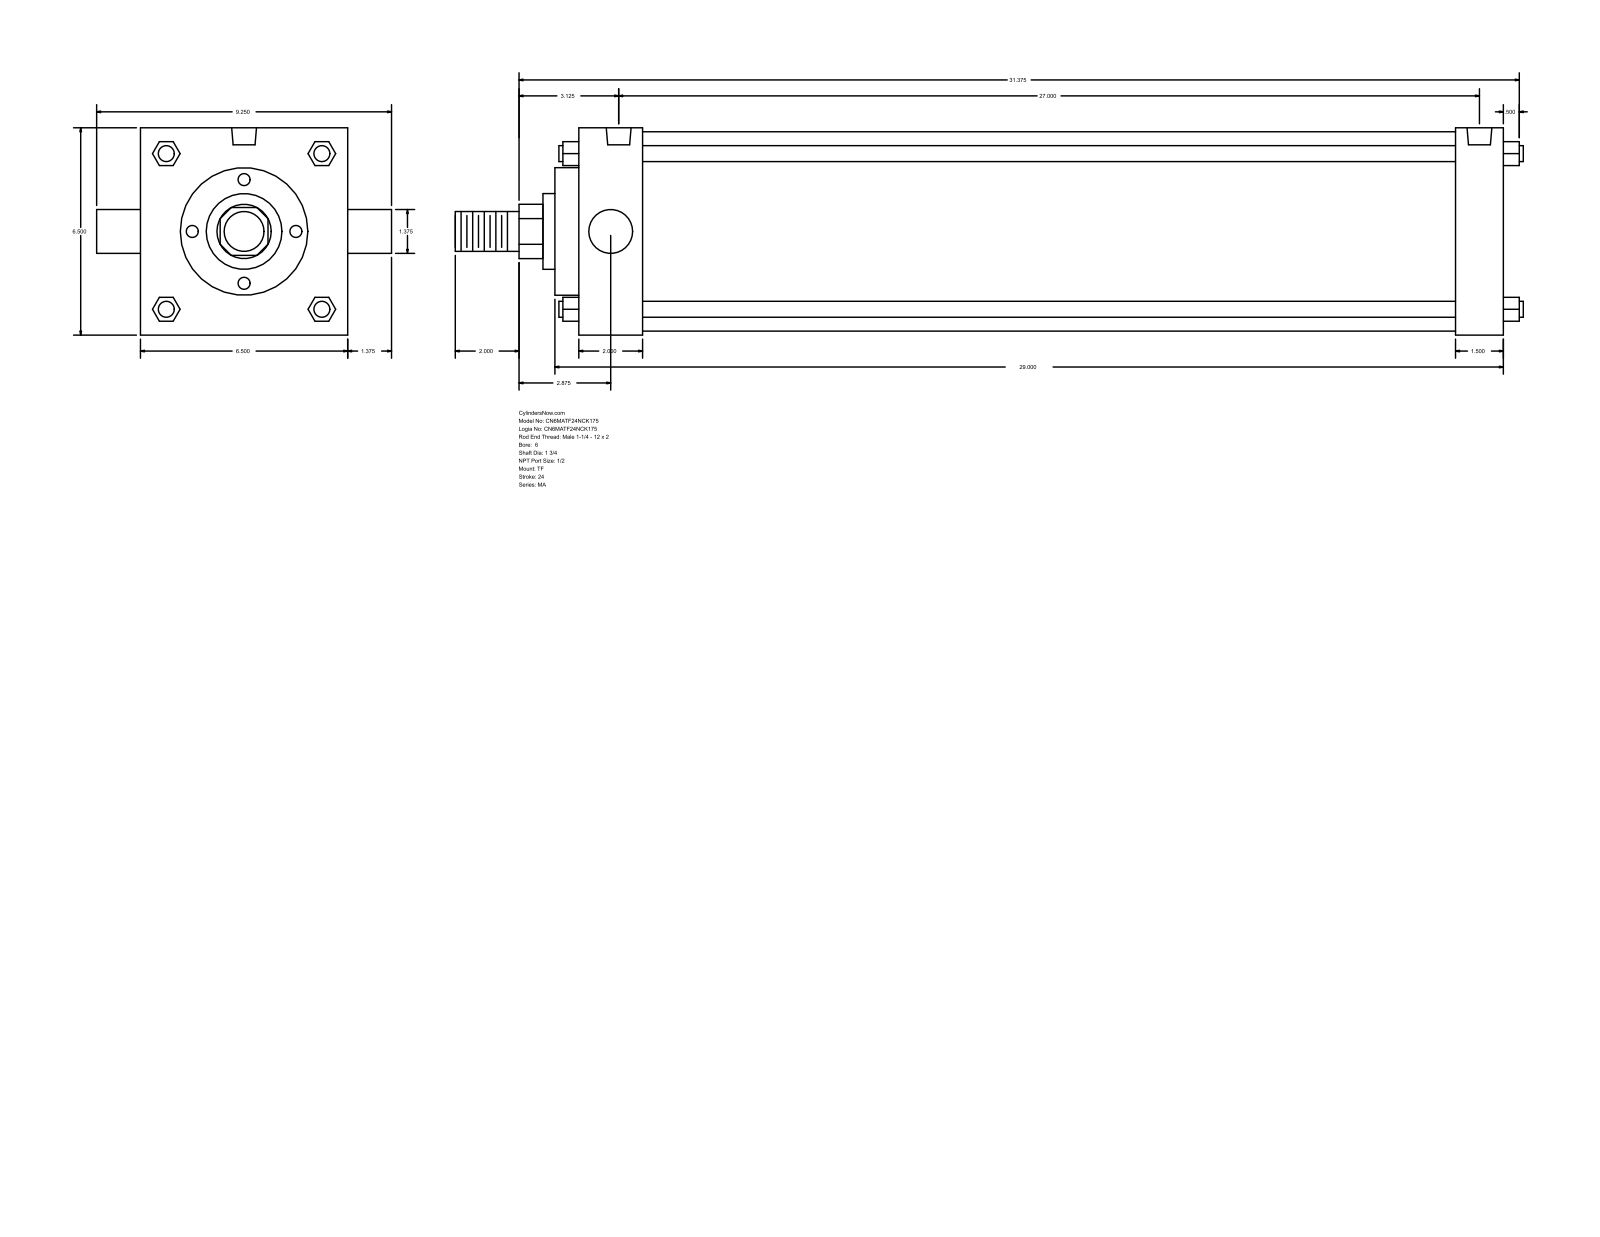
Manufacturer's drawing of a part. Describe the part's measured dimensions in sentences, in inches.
The part is named "MA_TF__0600_1.75". Its 3-D file was written by "GSSL Pune (CONFIG_CONTROL_DESIGN)". It is 0 solids with 122 faces: 93 planar, 29 cylindrical and 0 other. Overall it measures 33.5 by 9.25 by 6.5 inches. Round holes: 3 of diameter 0.687, 2 of diameter 0.778. Round bosses or shafts: 4 of diameter 0.5, 1 of diameter 6.25, 1 of diameter 4, 1 of diameter 2.375, 1 of diameter 1.75, 1 of diameter 1.375, 1 of diameter 1.25. Partial cylindrical surfaces (rounded edges, fillets, slot ends): 1 of radius 0.852. The main face-to-face distances are 6.5, 29, 0.75, 2, 27.5, 27, 25.5, 1.5, 2.75, 28.25. The hole center spacings are 27.
